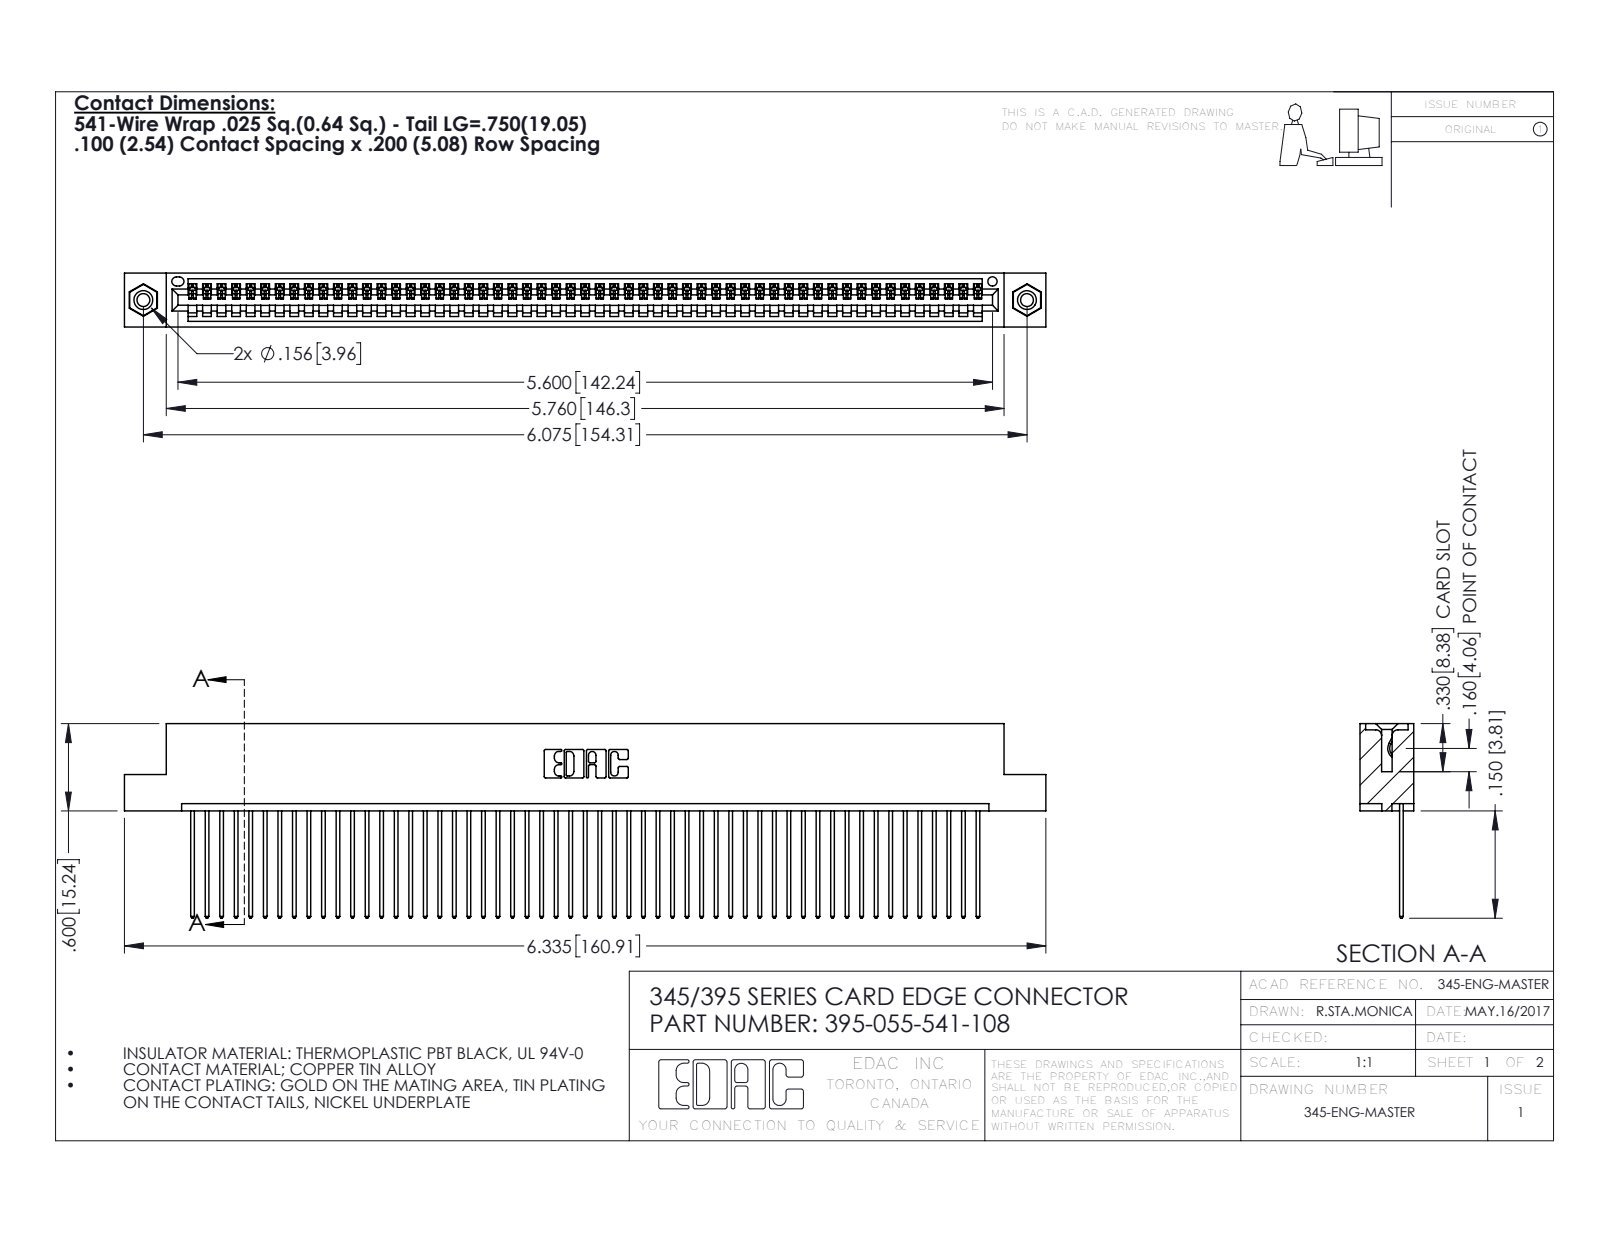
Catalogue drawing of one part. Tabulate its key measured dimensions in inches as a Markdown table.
| quantity | value |
| --- | --- |
| part name | 345-250-001_345-250-003-102; 395-055-541-108; 345-292-001_345-293-141; 345 Part_Flush Mounting Lugs - 0.156 Dia-TI |
| STEP written by | SolidWorks 2016 (CONFIG_CONTROL_DESIGN) |
| units | inches |
| bodies | 58 solids, 3376 faces (2312 planar, 1048 cylindrical, 16 other) |
| overall size | 6.335 × 1.337 × 0.37 |
| volume | 0.95 in³ |
| surface area | 34.02 in² |
| round holes (diameter × count) | 0.089 × 2, 0.125 × 2, 0.156 × 2, 0.064 × 1 |
| round bosses / shafts (diameter × count) | 0.155 × 2 |
| partial cylindrical surfaces (radius × count) | 0.006 × 110, 0.01 × 110, 0.01 × 22, 0.007 × 6, 0.031 × 6, 0.026 × 3, 0.031 × 2, 0.04 × 2 |
| main face-to-face distances | 0.072, 0.298, 0.098, 0.272, 0.025, 0.37, 0.2, 0.225, 0.149, 0.072 |
| hole center spacings | 0.27, 5.839, 6.075 |
